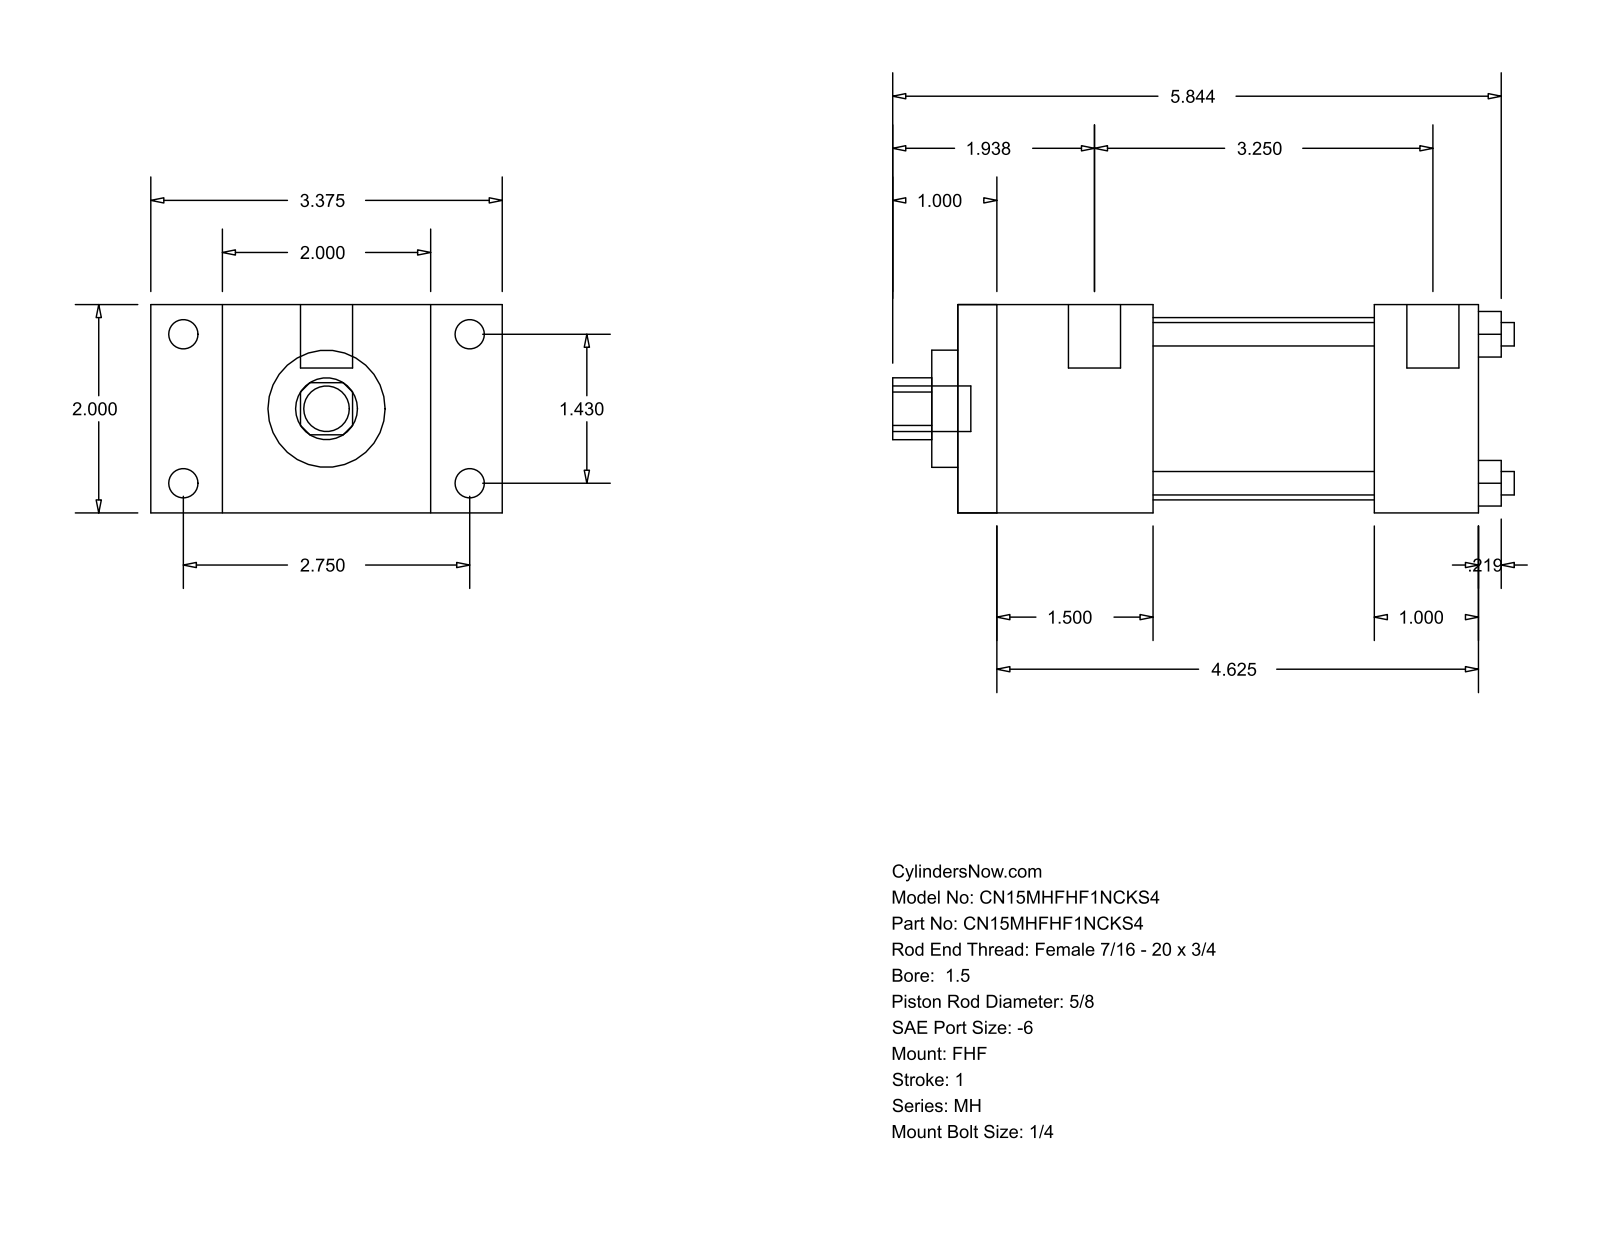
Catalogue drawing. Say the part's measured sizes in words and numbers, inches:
The part is named "MH_FHF__0150_0.625". Its 3-D file was written by "GSSL Pune (CONFIG_CONTROL_DESIGN)". It is 0 solids with 88 faces: 60 planar, 28 cylindrical and 0 other. Overall it measures 5.969 by 3.375 by 2 inches. Round holes: 4 of diameter 0.225, 1 of diameter 0.625, 1 of diameter 1.125, 1 of diameter 1.75. Round bosses or shafts: 4 of diameter 0.281, 4 of diameter 0.219, 2 of diameter 0.5, 1 of diameter 0.437. Partial cylindrical surfaces (rounded edges, fillets, slot ends): 1 of radius 0.297. The main face-to-face distances are 2, 0.687, 2.687, 1.875, 3.375, 5, 3.125, 2.125, 4, 1. The hole center spacings are 1.011, 1.43, 2.022.
